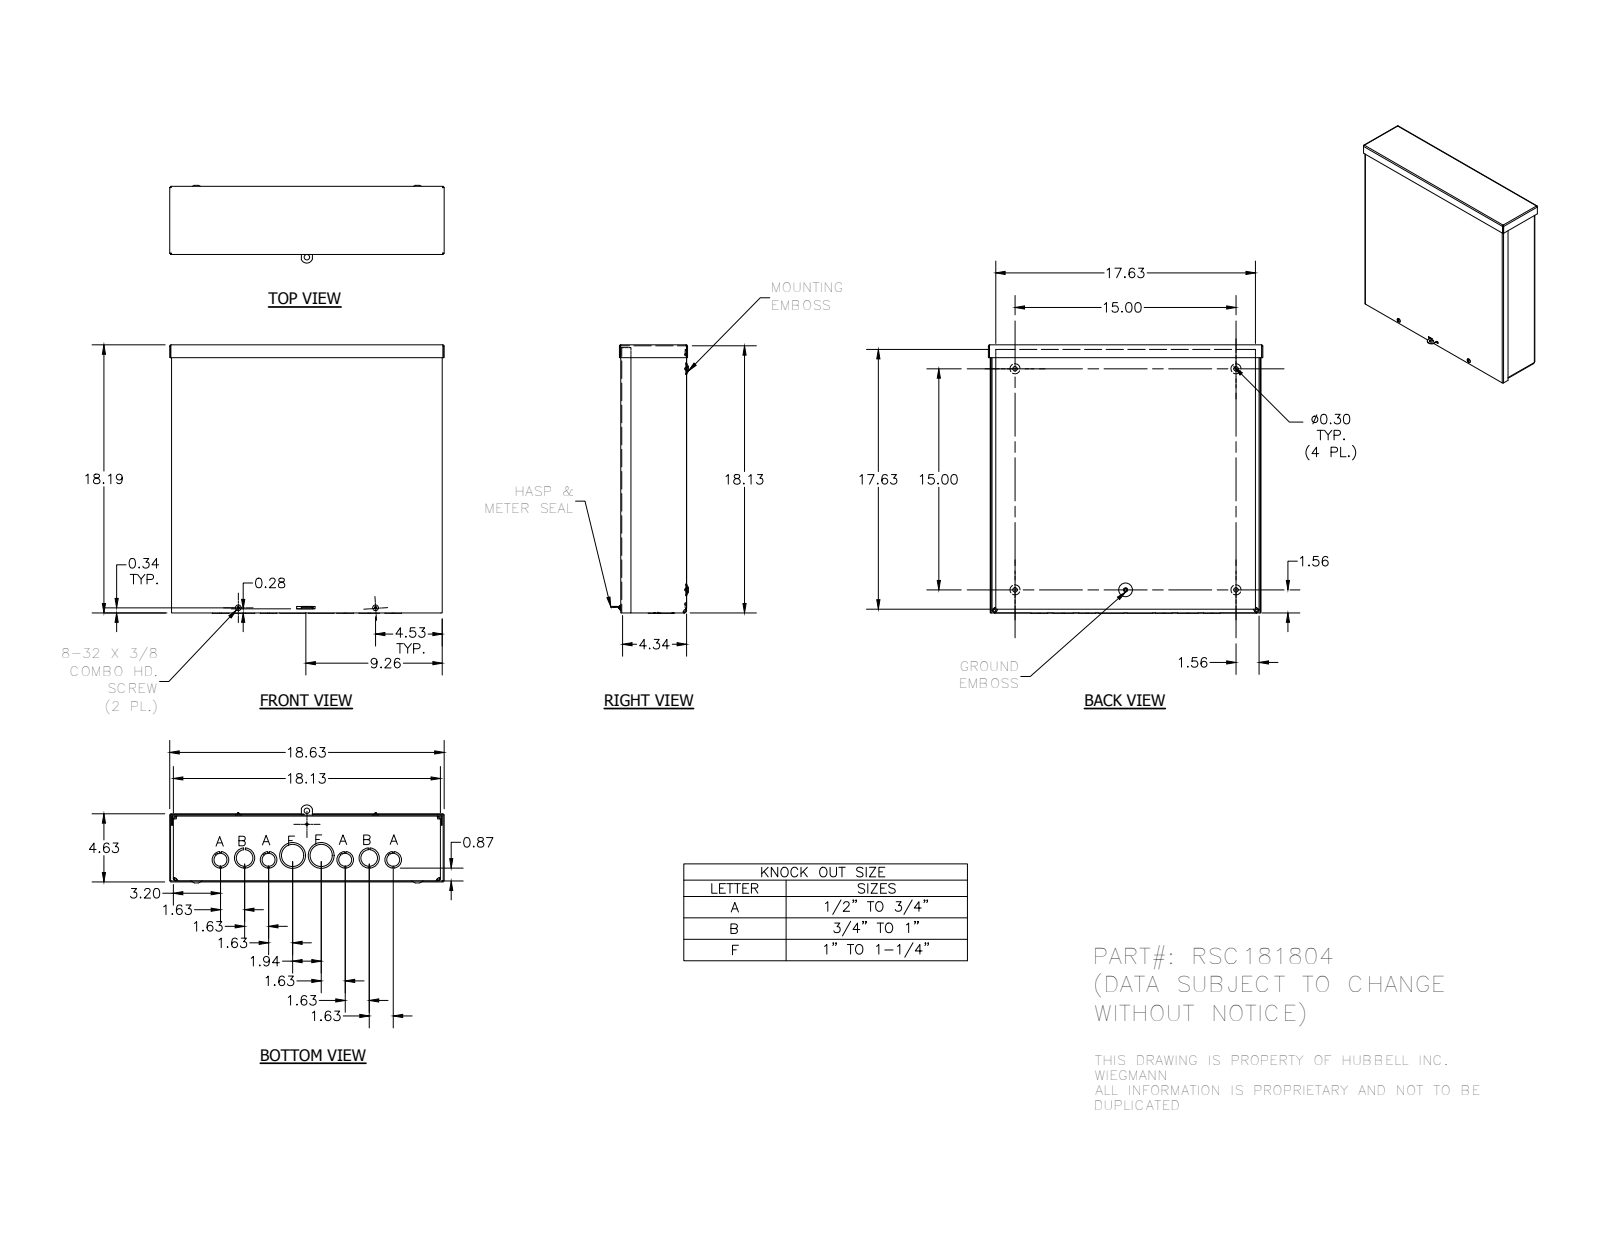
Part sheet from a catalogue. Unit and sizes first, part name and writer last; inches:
Units: inches
Overall size (bounding box): 18.625 × 18.281 × 5.125
Round holes (diameter × count): ⌀1.125 ×6, ⌀0.3 ×4, ⌀0.313 ×4, ⌀0.875 ×4, ⌀0.125 ×2, ⌀0.148 ×2, ⌀1.375 ×2, ⌀1.5 ×2, ⌀1.75 ×2, ⌀0.156 ×1, ⌀0.165 ×1, ⌀0.375 ×1
Round bosses / shafts (diameter × count): ⌀0.384 ×2, ⌀0.164 ×2, ⌀0.229 ×1
Partial cylindrical surfaces — rounded edges, fillets, slot ends (radius × count): R0.01 ×15, R0.031 ×8, R0.093 ×8, R0.125 ×8, R0.187 ×8, R0.031 ×5, R0.021 ×4, R0.055 ×4
Main face-to-face distances: 0.062, 4.249, 4.187, 0.063, 4.312, 4.25, 18.126, 0.062, 18.188, 0.124
Hole centre spacings: 1.635, 15, 8.46, 1.656, 3.031, 3.26, 3.264, 3.582
Volume: 74 in³ · Surface area: 2 410 in²
Bodies: 7 solids, 619 faces (304 planar, 171 cylindrical, 144 other)
Part name (STEP PRODUCT): RSC181804; RSC181804_WRAP; RSC1818_LID; RSC1804_CAP (+4 more)
STEP written by: Autodesk Inventor 2012 (AUTOMOTIVE_DESIGN)
